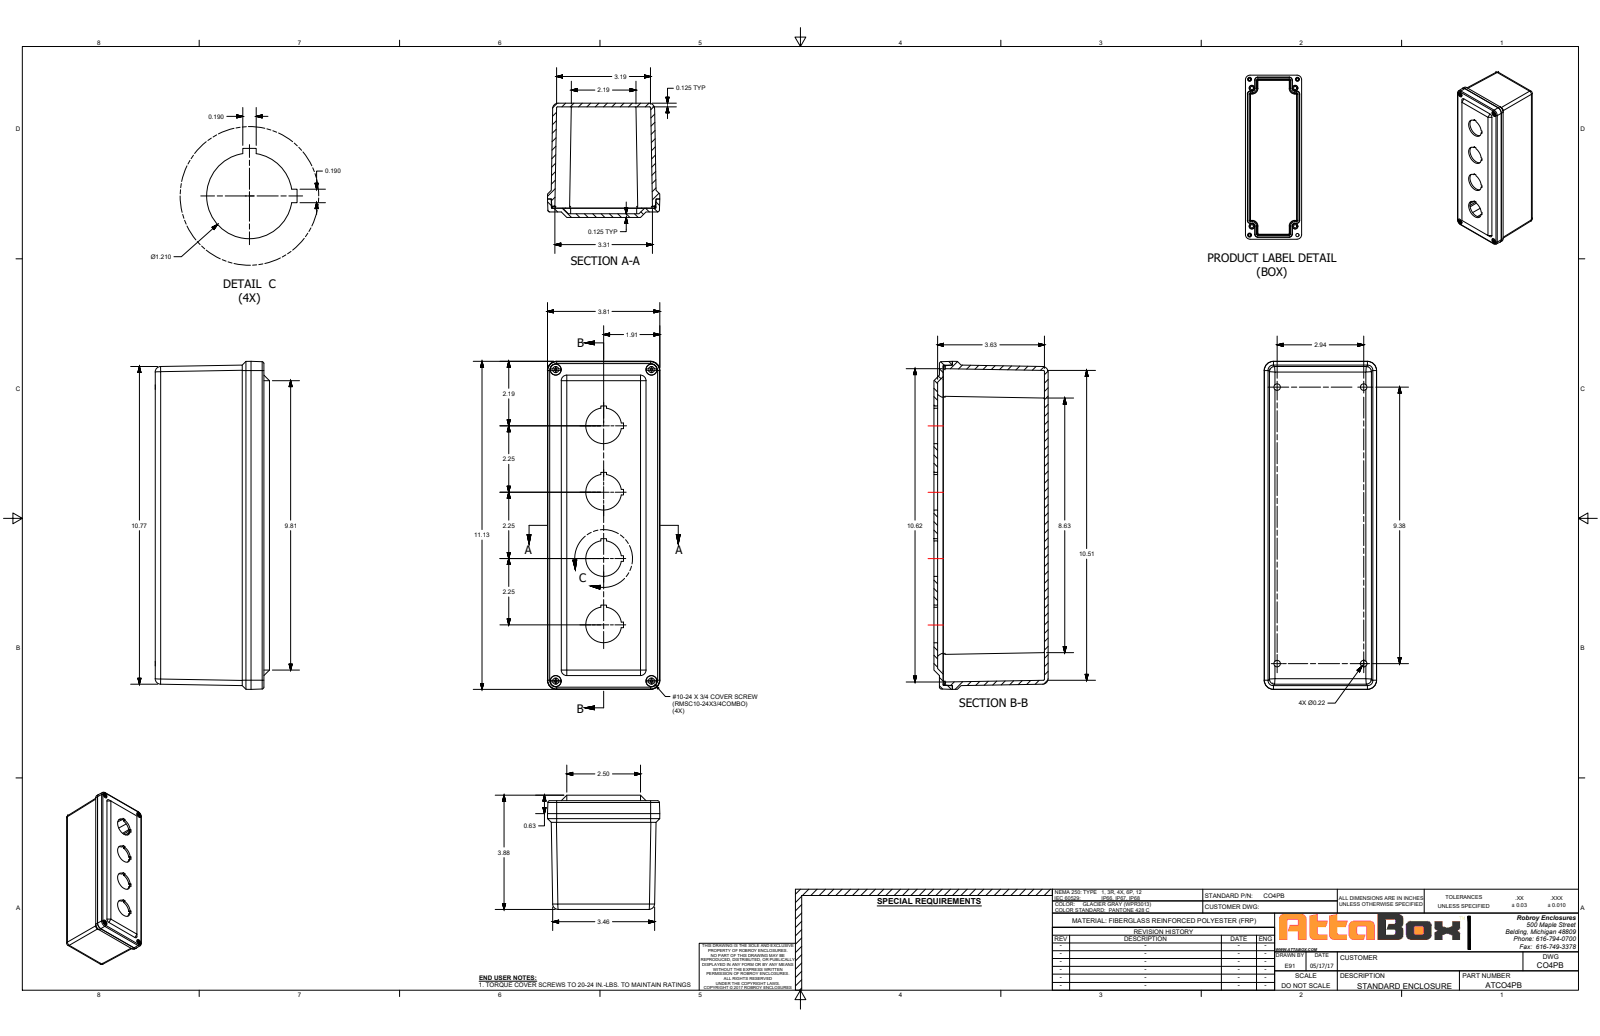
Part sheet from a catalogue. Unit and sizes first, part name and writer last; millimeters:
Units: millimetres
Overall size (bounding box): 282.6 × 98.4 × 96.9
Round holes (diameter × count): ⌀5.6 ×8, ⌀4 ×4, ⌀4.8 ×4, ⌀9.5 ×4, ⌀30.7 ×4
Round bosses / shafts (diameter × count): ⌀9.4 ×4, ⌀6.9 ×4, ⌀4.5 ×4
Partial cylindrical surfaces — rounded edges, fillets, slot ends (radius × count): R0.8 ×20, R0.3 ×16, R1.6 ×4, R4.5 ×4, R4.8 ×4, R5.6 ×4, R7.9 ×4, R8.3 ×4
Main face-to-face distances: 3.2, 3.3, 95.3, 4.7, 90.5, 98.4, 92.1, 12.7, 1.6, 93.6
Hole centre spacings: 15.6, 113.4, 167.9, 223.7, 253.2, 268.3, 50, 63.6
Volume: 467 000 mm³ · Surface area: 257 500 mm²
Bodies: 11 solids, 411 faces (207 planar, 108 cylindrical, 96 other)
Part name (STEP PRODUCT): CO4PB
STEP written by: SolidWorks 2018 (AUTOMOTIVE_DESIGN)
